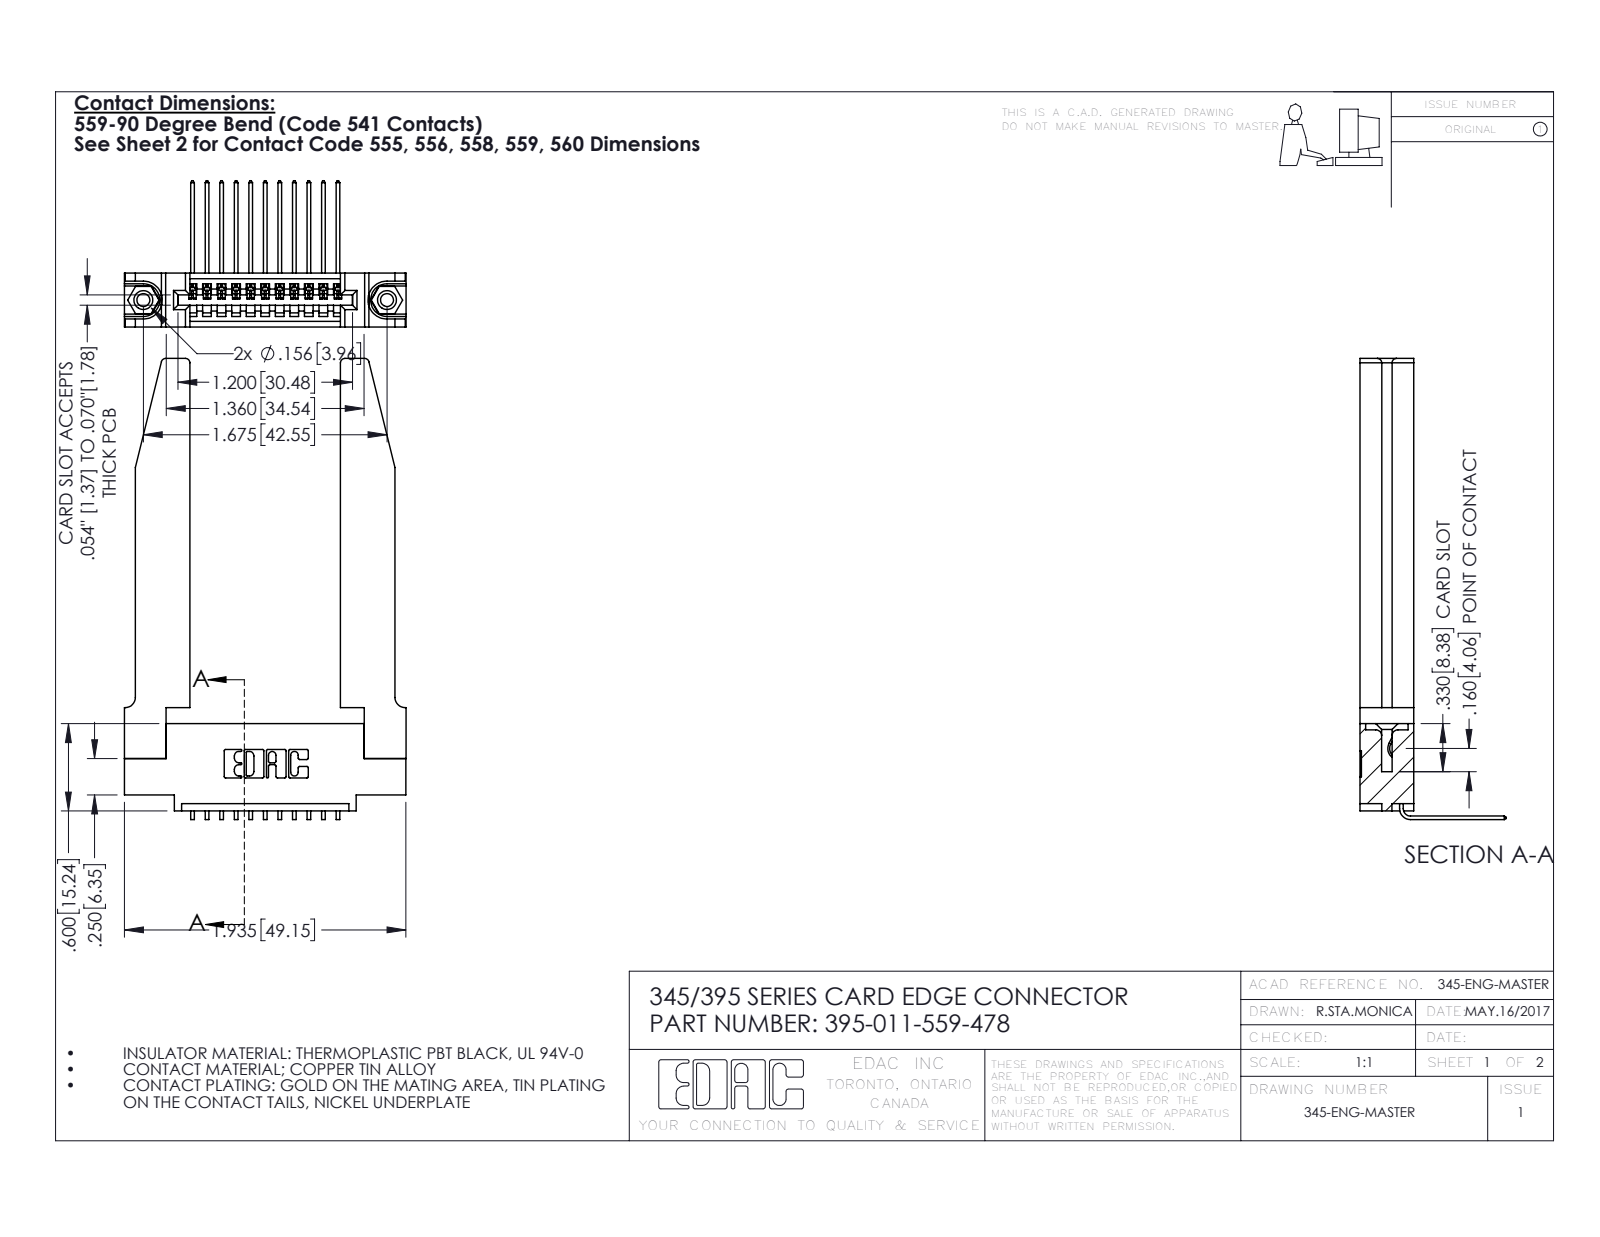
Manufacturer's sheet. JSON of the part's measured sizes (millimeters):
{"part_name": "395-011-559-478; 345-292-001_558 559 Tail - 1; 345-250-001_345-250-001-102; 345-220-078_345-220-078 (+1 more)", "step_written_by": "SolidWorks 2016 (CONFIG_CONTROL_DESIGN)", "units": "millimeters", "bodies": {"solids": 16, "faces": 1024, "planar": 688, "cylindrical": 284, "other": 52}, "overall_size": [80.5, 49.2, 25.5], "volume_mm3": 12100, "surface_area_mm2": 12540, "round_holes": [[2.3, 2], [3.2, 2], [4, 2], [1.6, 1]], "round_bosses_or_shafts": [[3.9, 2]], "partial_cylinders_radius": [[0.2, 22], [0.3, 22], [0.8, 8], [0.2, 6], [0.8, 6], [0.7, 3], [0.8, 2], [1, 2]], "face_to_face_distances": [9.4, 1.8, 7.6, 3.8, 3.8, 5.6, 2, 26.3, 5.1, 2.5], "hole_center_spacings": [6.9, 36.7, 42.5]}
